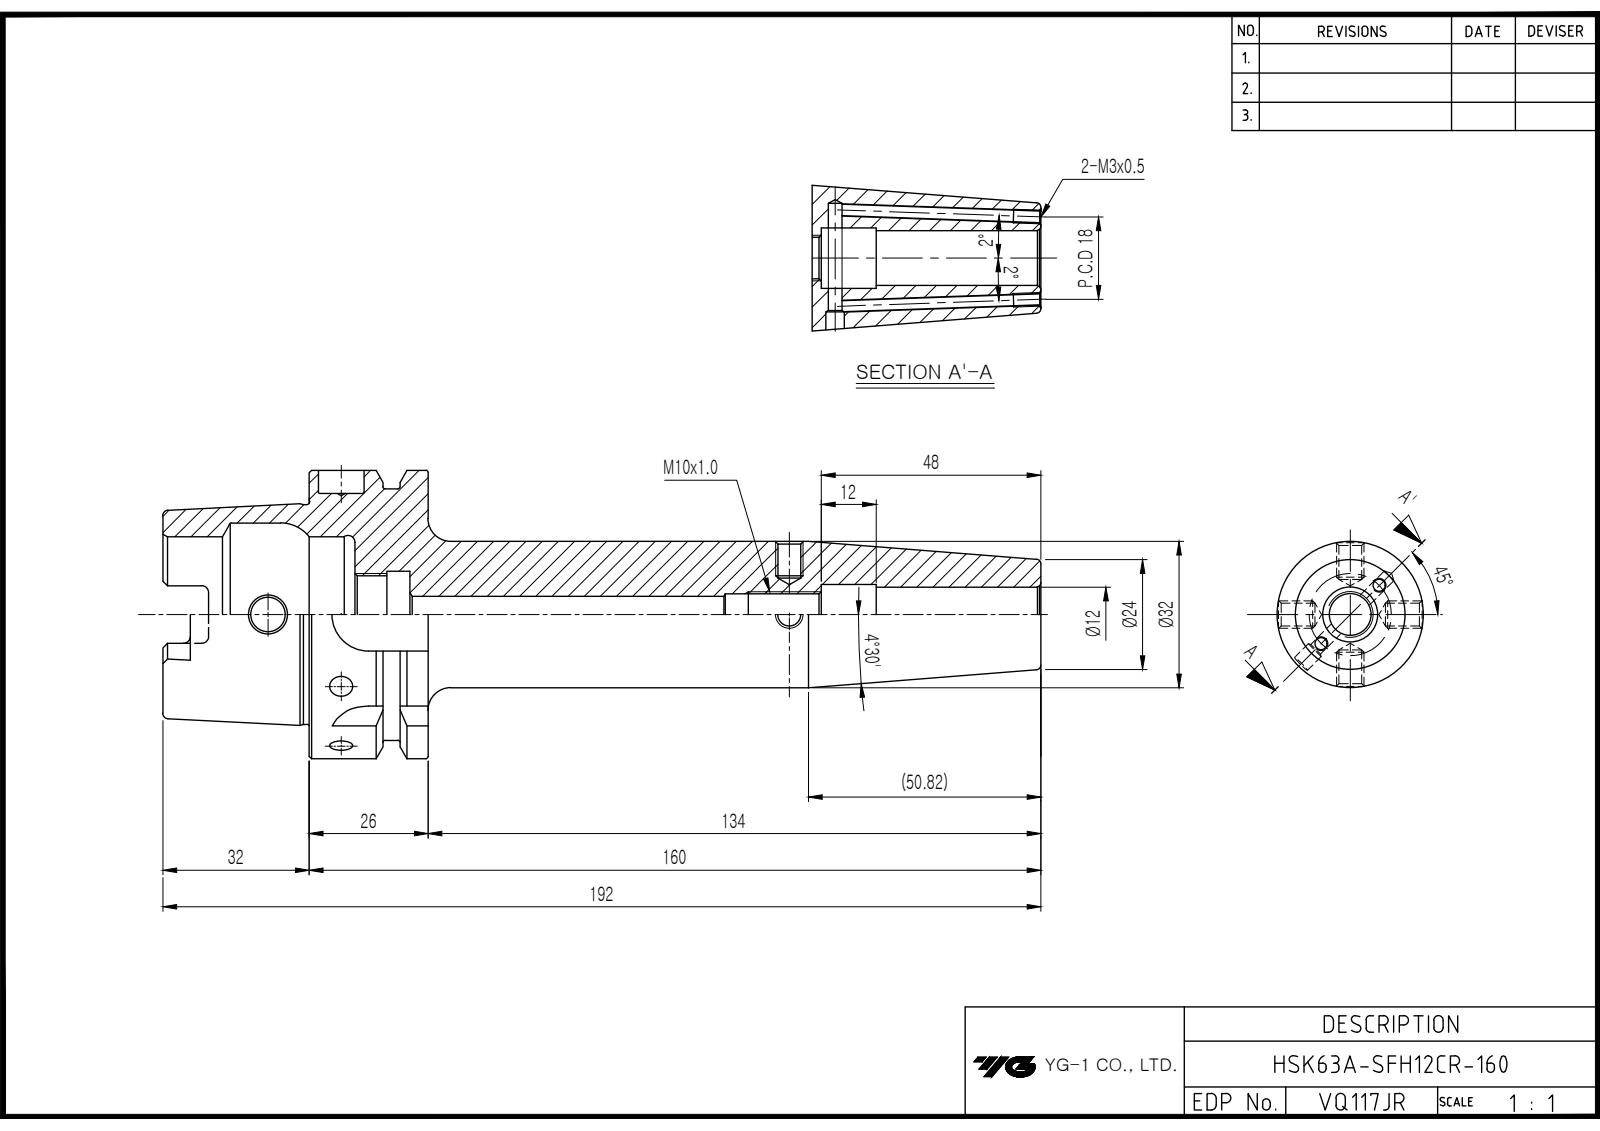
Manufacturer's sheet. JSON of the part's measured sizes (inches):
{"part_name": "LO-HSK63A-SFH12CR-160", "step_written_by": "Autodesk Inventor 2022 (AUTOMOTIVE_DESIGN)", "units": "inches", "bodies": {"solids": 1, "faces": 121, "planar": 42, "cylindrical": 36, "other": 43}, "overall_size": [7.559, 2.48, 2.48], "volume_in3": 10.36, "surface_area_in2": 60.98, "round_holes": [[0.097, 2], [0.295, 1], [0.315, 1], [0.351, 1], [0.394, 1], [0.472, 1], [0.52, 1], [0.666, 1], [0.748, 1], [1.339, 1], [1.575, 1]], "round_bosses_or_shafts": [[2.48, 1], [2.165, 1], [1.891, 1], [1.26, 1]], "partial_cylinders_radius": [[0.059, 6], [0.113, 4], [0.315, 4]], "face_to_face_distances": [1.024, 0.394, 0.63, 1.26, 1.654, 2.283, 2.087, 0.866, 0.472, 0.157]}
